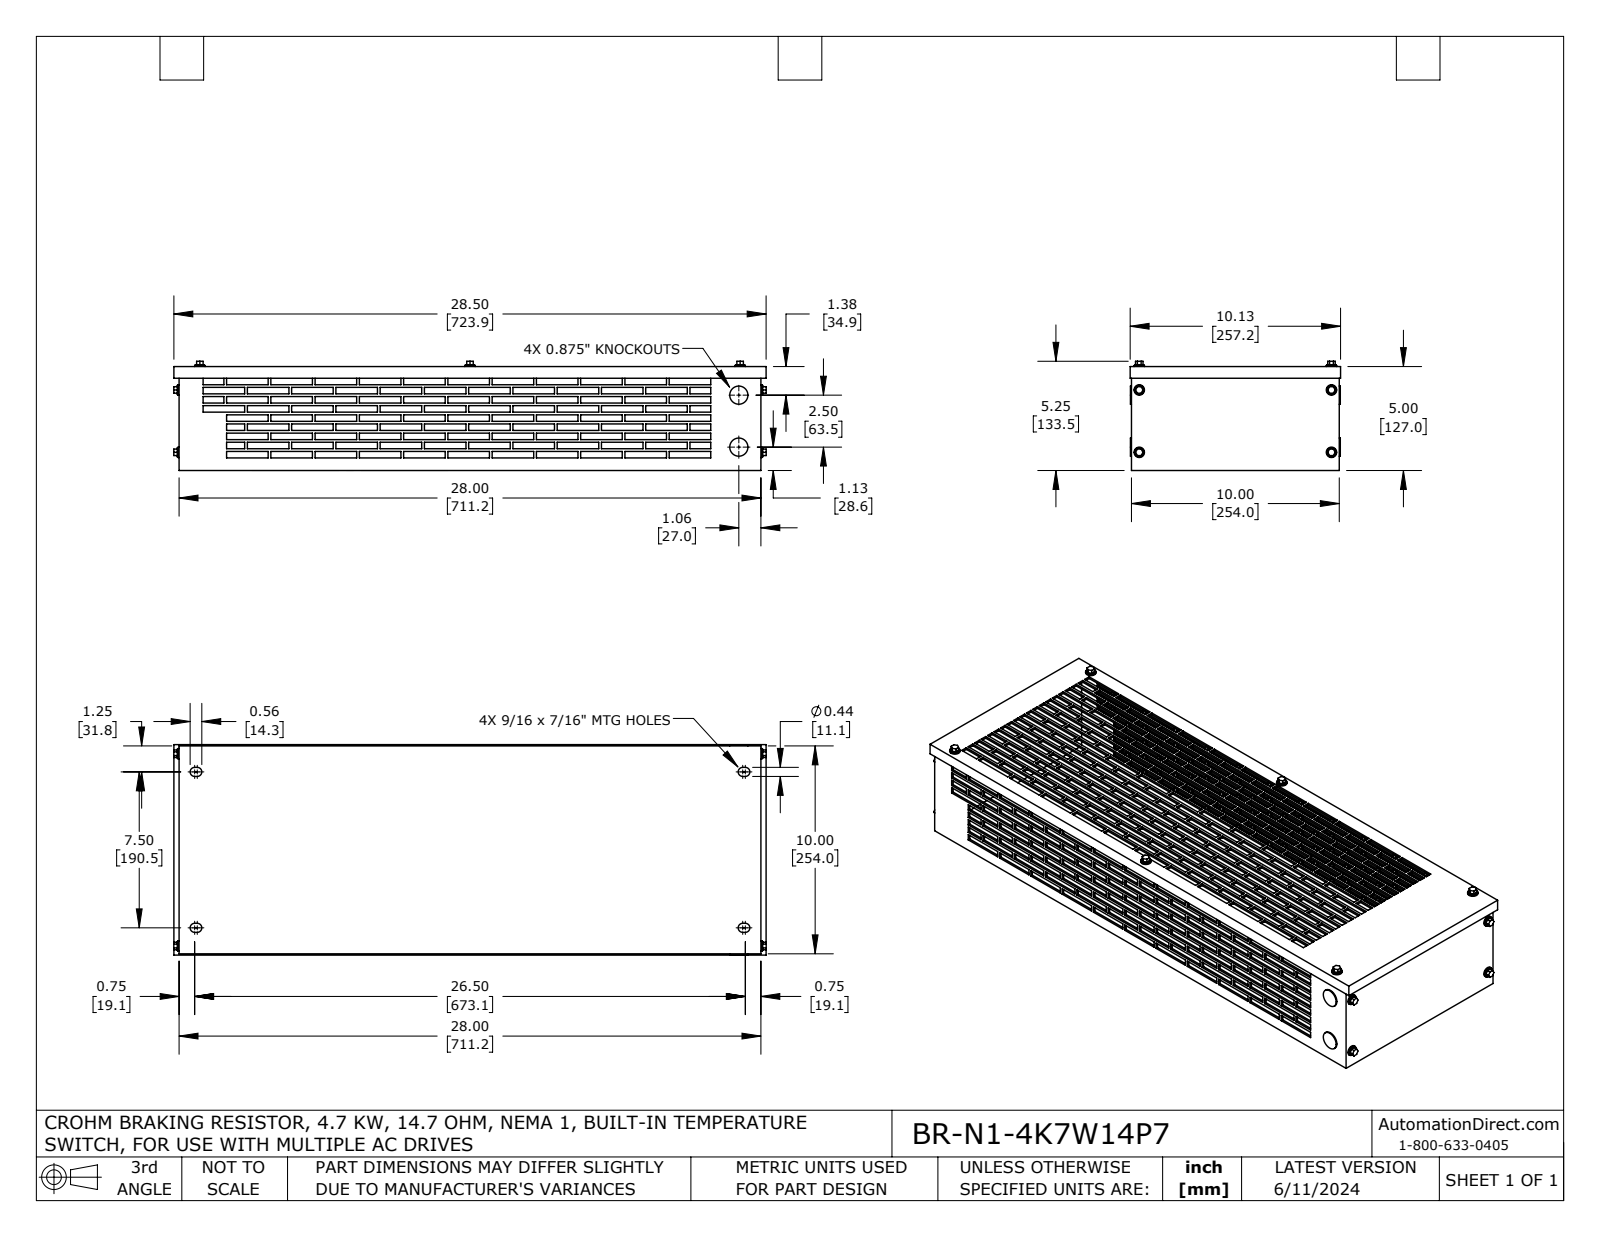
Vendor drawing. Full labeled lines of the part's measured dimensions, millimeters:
Part name (STEP PRODUCT): BR-N1-4K7W14P7
STEP written by: SolidWorks 2021 (AUTOMOTIVE_DESIGN)
Units: millimetres
Bodies: 33 solids, 2040 faces (1932 planar, 108 cylindrical, 0 other)
Overall size (bounding box): 724.1 × 257.2 × 133.5
Volume: 1 115 000 mm³ · Surface area: 1 011 000 mm²
Round holes (diameter × count): ⌀6.4 ×10, ⌀19.1 ×2
Round bosses / shafts (diameter × count): ⌀12.7 ×10, ⌀11.1 ×10, ⌀22.2 ×2
Partial cylindrical surfaces — rounded edges, fillets, slot ends (radius × count): R5.6 ×8
Main face-to-face distances: 2.5, 124.5, 127, 121.9, 251.5, 708.7, 254, 248.9, 22.4, 1.6
Hole centre spacings: 235, 330.2, 405.3, 76.2, 247, 660.4, 700.9, 63.5
